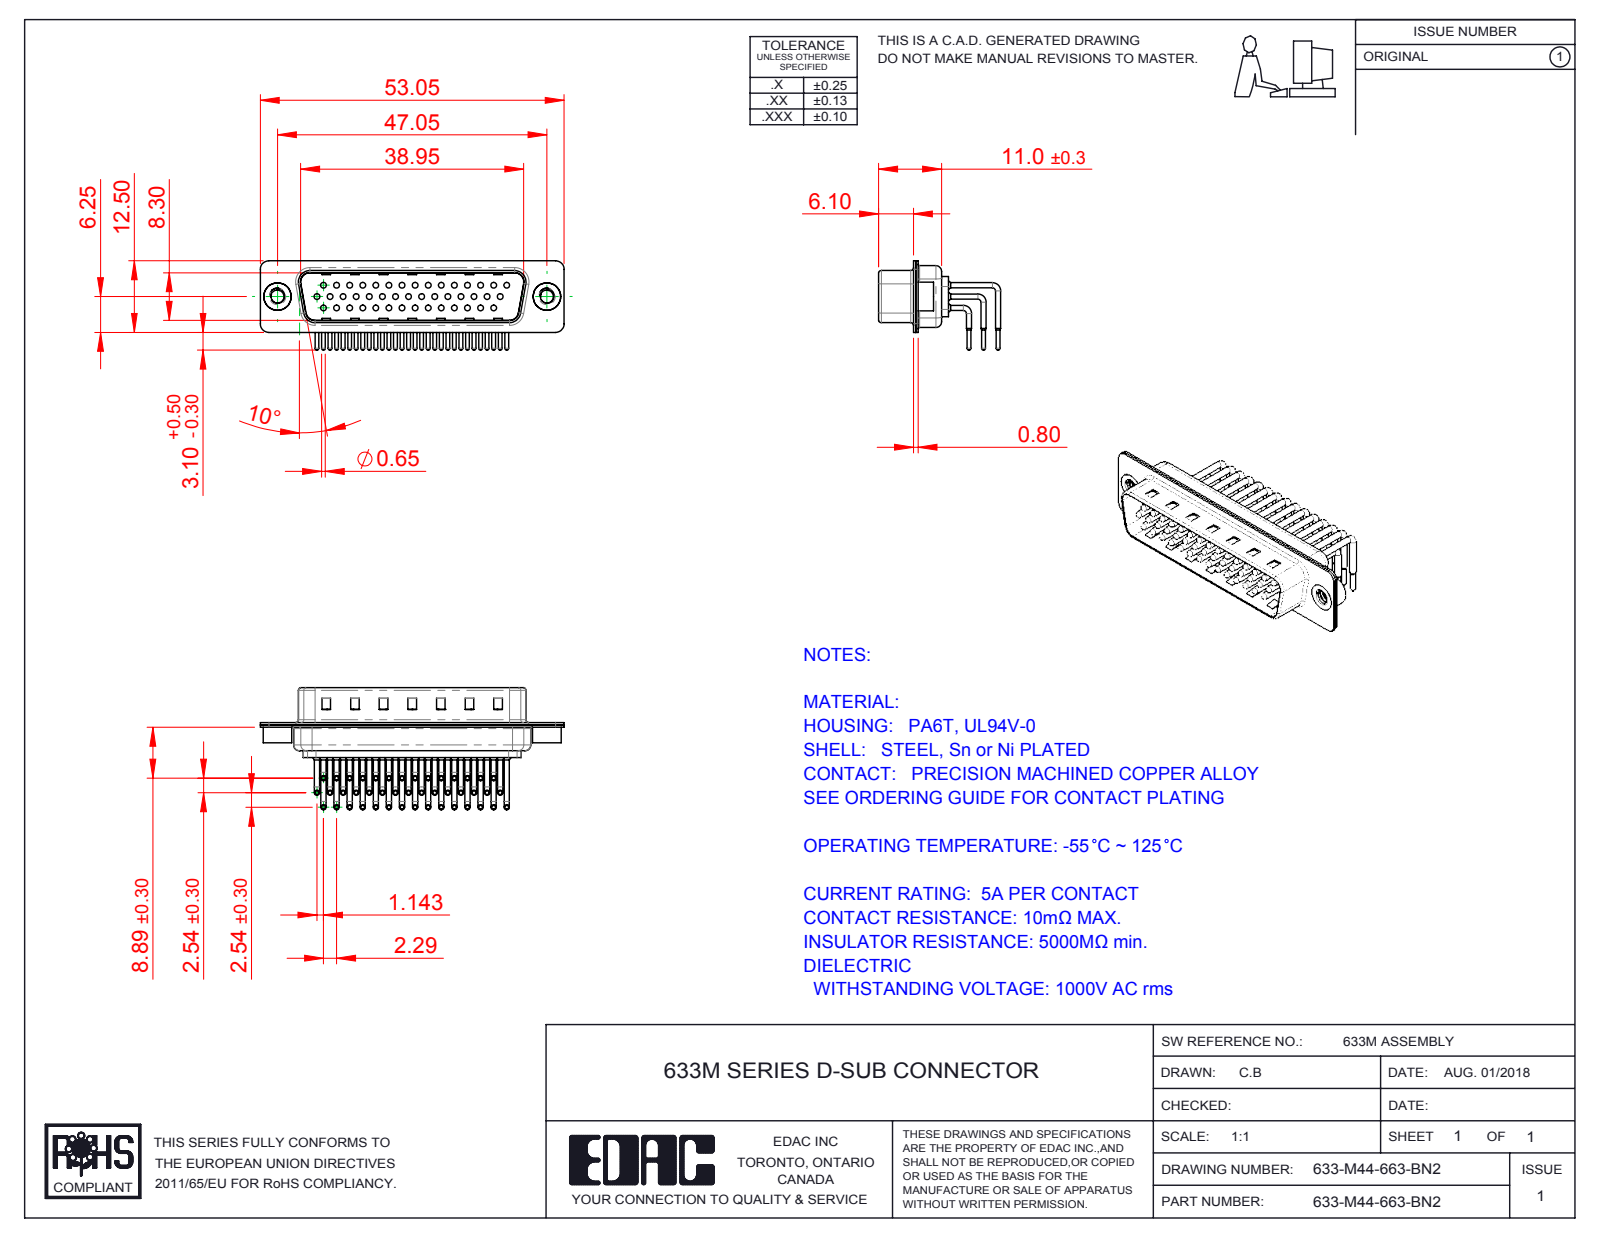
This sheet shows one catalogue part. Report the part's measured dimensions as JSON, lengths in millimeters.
{"part_name": "633M 4-40 Threaded Rivet; 633M Housing_44 Contacts; 633M Shell Front_44 Contacts; 633M Shell Rear_44 Contacts (+4 more)", "step_written_by": "SolidWorks 2016 (CONFIG_CONTROL_DESIGN)", "units": "millimeters", "bodies": {"solids": 49, "faces": 5216, "planar": 2987, "cylindrical": 1721, "other": 508}, "overall_size": [53.05, 21.32, 15.6], "volume_mm3": 3136, "surface_area_mm2": 10056, "round_holes": [[1, 44], [1.7, 44], [2, 44], [2.26, 2], [4, 2], [4.8, 2]], "round_bosses_or_shafts": [[0.9, 88], [1.5, 44], [0.65, 44], [5, 2], [4.9, 2], [1, 2]], "partial_cylinders_radius": [[1.01, 44], [1.5, 16], [2, 12], [0.5, 8], [1.6, 8], [0.25, 4], [0.6, 4], [0.65, 4]], "face_to_face_distances": [0.4, 0.85, 9.55, 1.5, 8.7, 1.9, 1.25, 10.4, 0.35, 9.15], "hole_center_spacings": [2.28, 3.96, 2.29, 4.57, 8.24, 6.86, 11.43, 12.72]}
